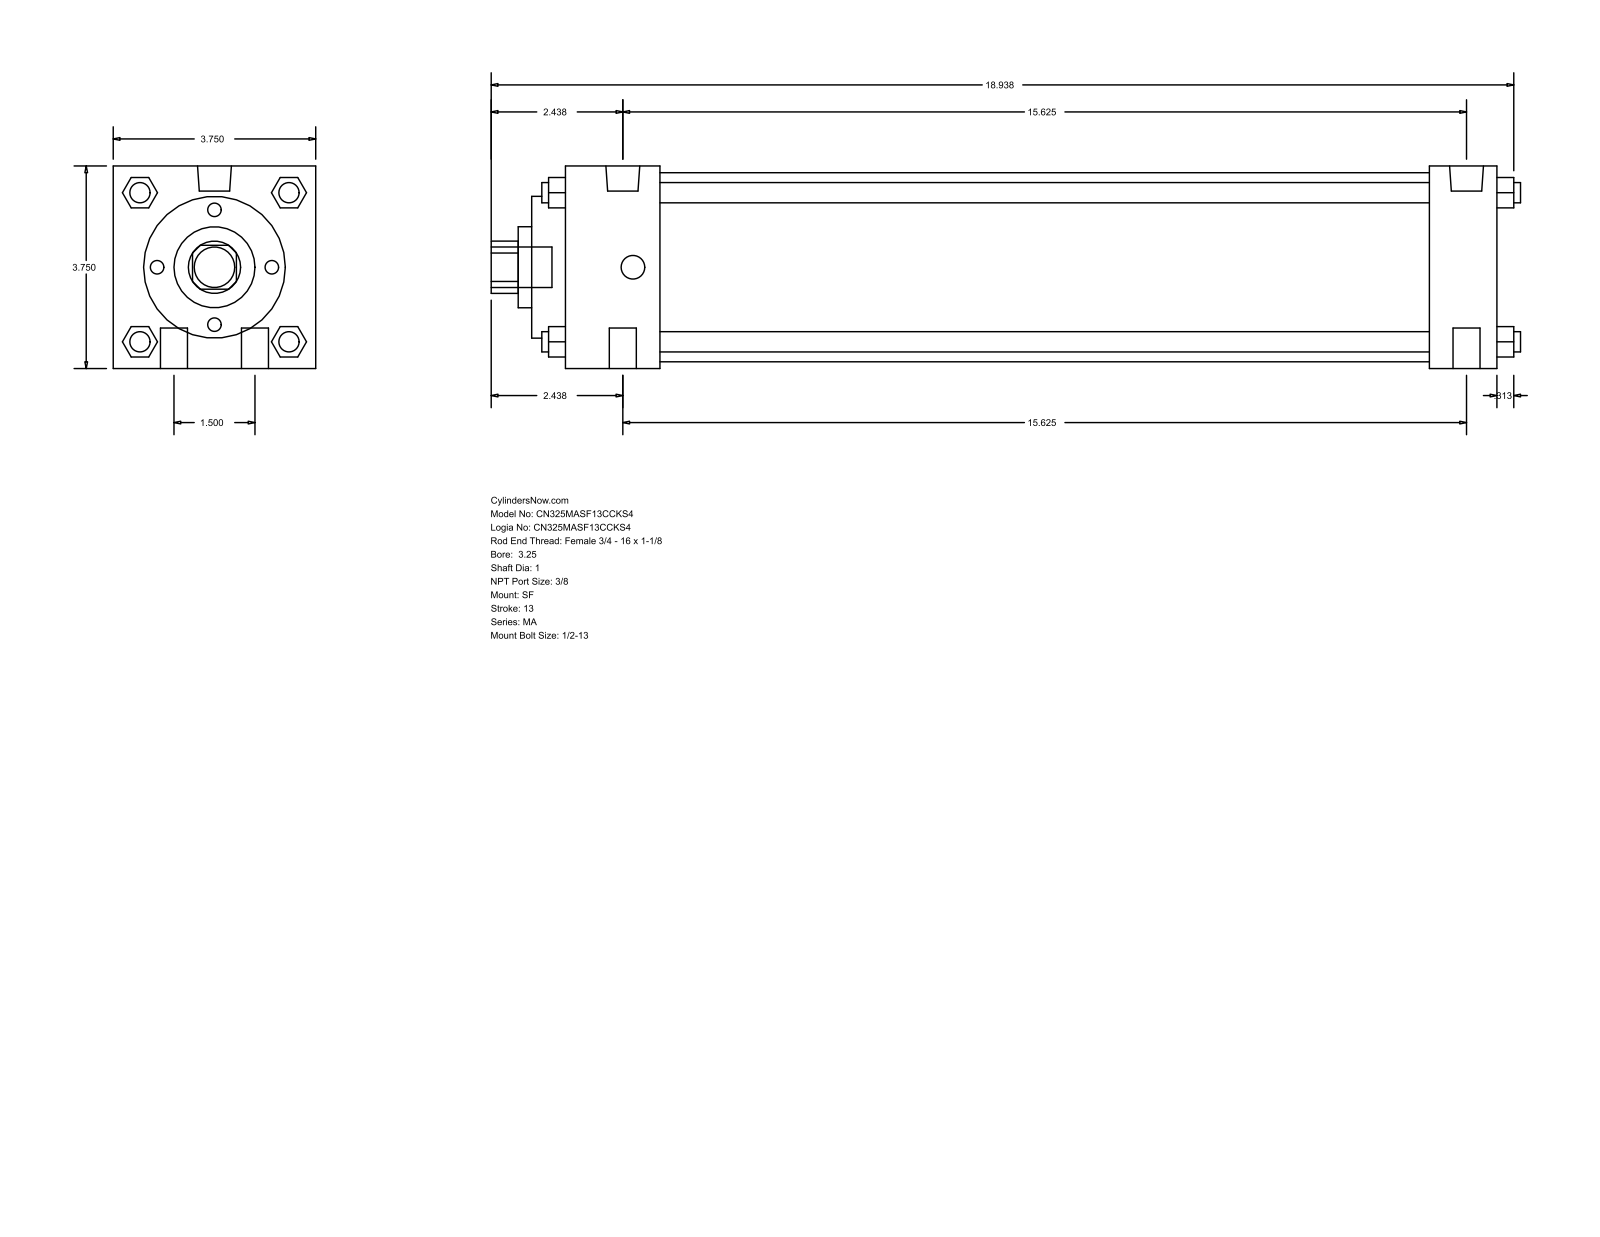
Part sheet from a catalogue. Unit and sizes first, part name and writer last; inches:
Units: inches
Overall size (bounding box): 19.063 × 3.75 × 3.75
Round holes (diameter × count): ⌀1 ×1, ⌀1.5 ×1, ⌀2.625 ×1, ⌀3.5 ×1
Round bosses / shafts (diameter × count): ⌀0.5 ×4, ⌀0.375 ×4, ⌀0.627 ×2, ⌀0.437 ×2, ⌀0.75 ×1
Partial cylindrical surfaces — rounded edges, fillets, slot ends (radius × count): R0.484 ×1
Main face-to-face distances: 3.75, 17.25, 17.875, 0.625, 16, 1.25, 1.75, 14.25, 15.5, 2.375
Bodies: 0 solids, 126 faces (95 planar, 31 cylindrical, 0 other)
Part name (STEP PRODUCT): MA_SF__0325_1
STEP written by: GSSL Pune (CONFIG_CONTROL_DESIGN)
